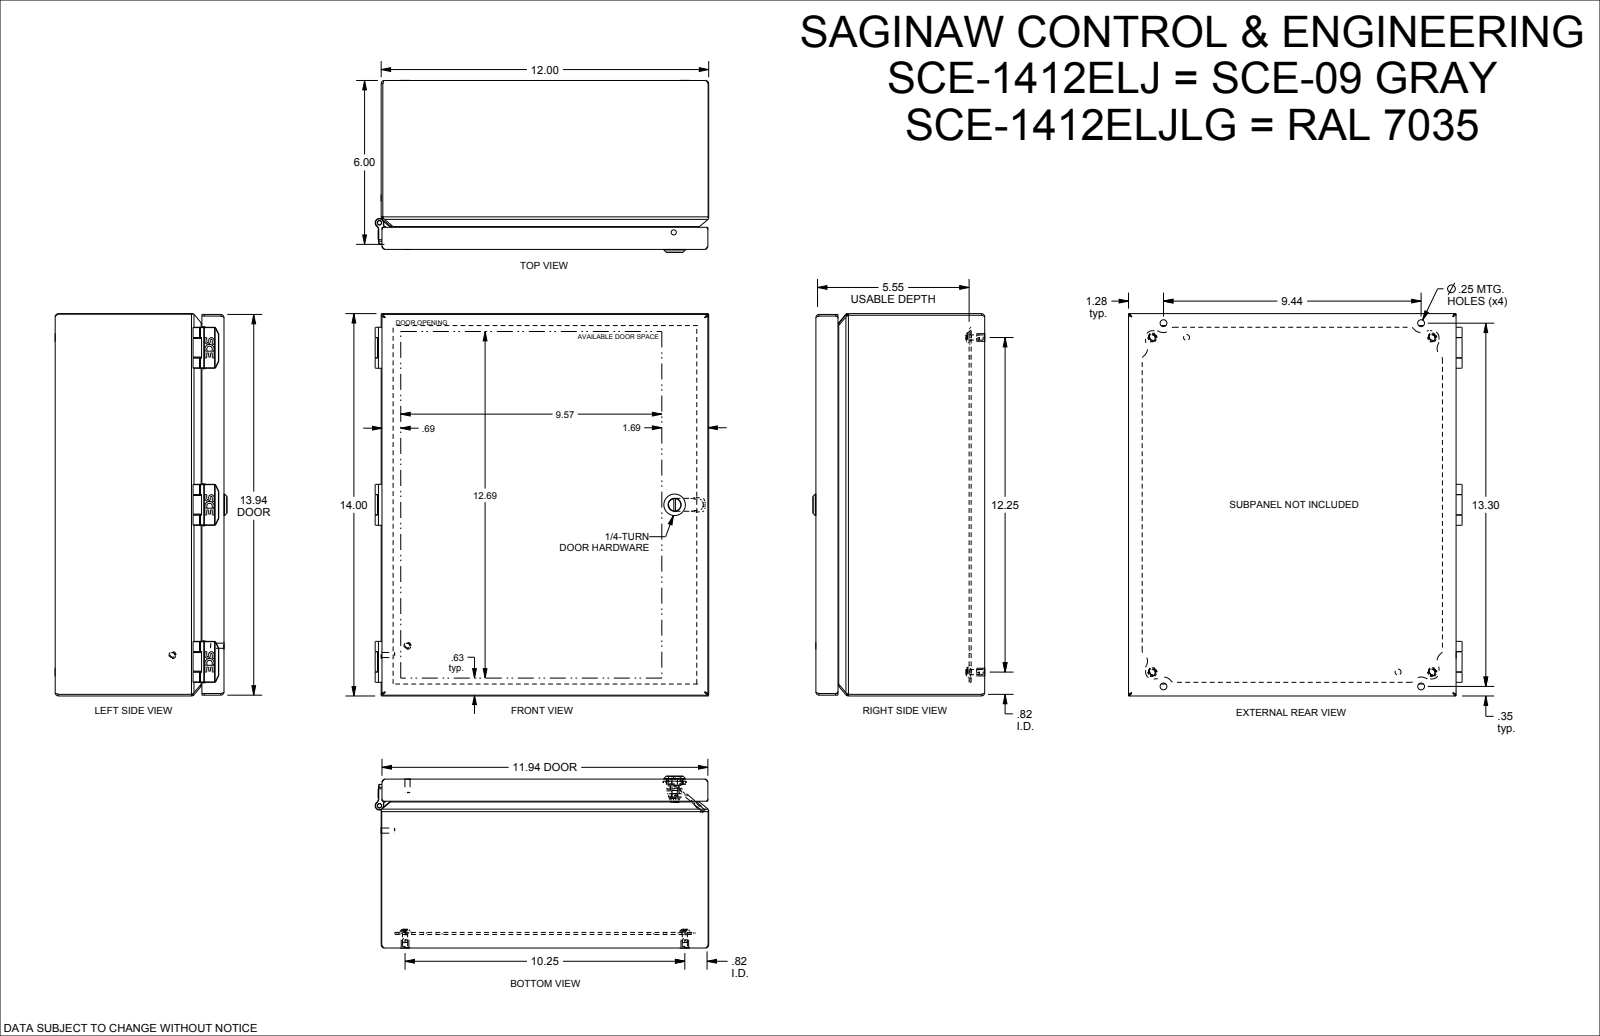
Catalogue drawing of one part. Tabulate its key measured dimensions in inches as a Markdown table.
| quantity | value |
| --- | --- |
| part name | SCE-1412ELJ |
| STEP written by | SolidWorks 2019 (AUTOMOTIVE_DESIGN) |
| units | inches |
| bodies | 35 solids, 1114 faces (406 planar, 387 cylindrical, 321 other) |
| overall size | 14.06 × 12.22 × 6.296 |
| volume | 56.06 in³ |
| surface area | 1 757 in² |
| round holes (diameter × count) | 0.19 × 4, 0.25 × 4, 0.284 × 4, 0.02 × 3, 0.1 × 3, 0.218 × 2, 0.266 × 2, 0.158 × 1, 0.196 × 1, 0.2 × 1, 0.239 × 1, 0.254 × 1 |
| round bosses / shafts (diameter × count) | 0.188 × 6, 0.16 × 6, 0.373 × 4, 0.28 × 4, 0.26 × 3, 0.237 × 3, 0.23 × 3, 0.18 × 3 |
| partial cylindrical surfaces (radius × count) | 0.03 × 40, 0.013 × 31, 0.05 × 16, 0.25 × 13, 0.01 × 12, 0.062 × 12, 0.125 × 11, 0.06 × 10 |
| main face-to-face distances | 0.059, 0.06, 6.185, 6.126, 6.125, 6.066, 0.571, 0.512, 5.554, 5.614 |
| hole center spacings | 15.2, 0.06, 1.25, 5.75, 6.136, 9, 10.25, 10.25 |
